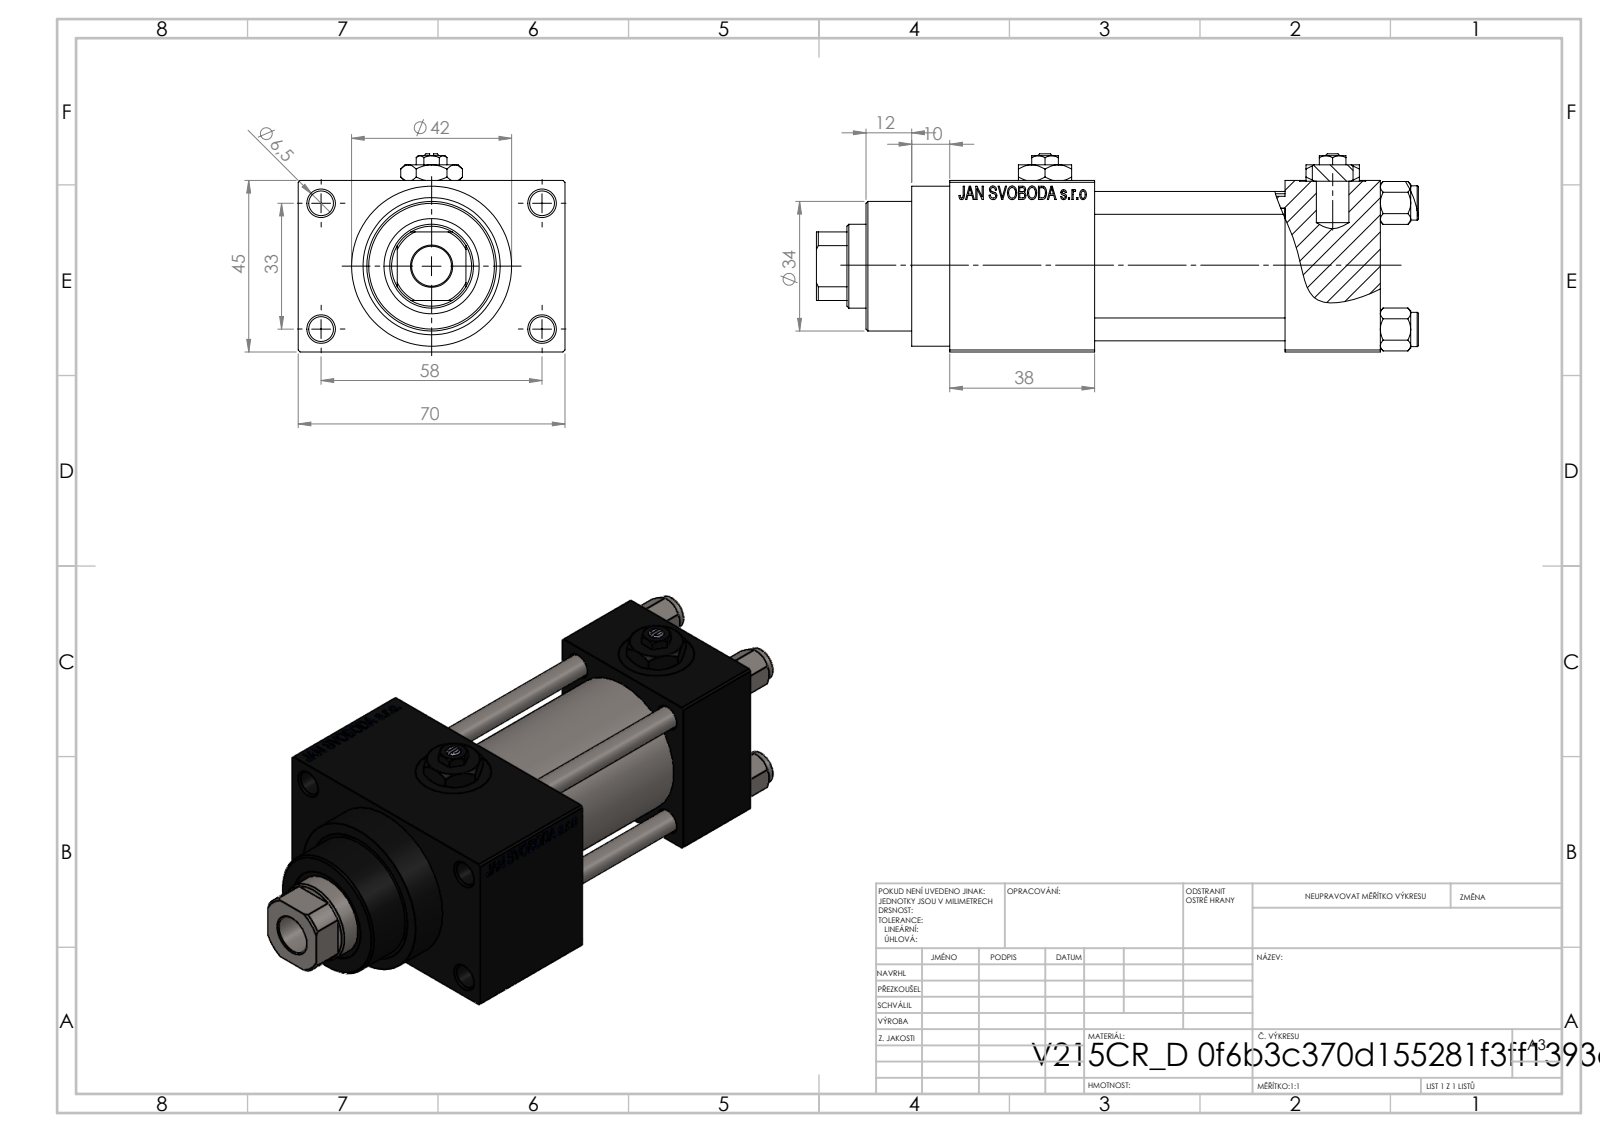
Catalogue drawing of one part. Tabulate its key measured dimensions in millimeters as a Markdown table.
| quantity | value |
| --- | --- |
| part name | NUT_M5_D; V215CR_D_Body; V215_VC_A; V215CR_VCP_D (+2 more) |
| STEP written by | SolidWorks 2019 (CONFIG_CONTROL_DESIGN) |
| units | millimeters |
| bodies | 13 solids, 1203 faces (542 planar, 99 cylindrical, 562 other) |
| overall size | 158 × 70 × 52 |
| volume | 241 625 mm³ |
| surface area | 81 624 mm² |
| round holes (diameter × count) | 6 × 4, 6.5 × 4, 13.16 × 4, 20 × 4, 7 × 3, 10.5 × 1, 22 × 1, 24 × 1, 25 × 1, 32 × 1, 33 × 1 |
| round bosses / shafts (diameter × count) | 9 × 4, 42 × 1, 38 × 1, 34 × 1 |
| partial cylindrical surfaces (radius × count) | 10.5 × 1 |
| main face-to-face distances | 45, 25, 50, 12.5, 75, 57.5, 88, 38, 113, 70 |
| hole center spacings | 12.4, 23.48, 33.2, 33.37, 35.35, 45.6, 56.35, 33 |
